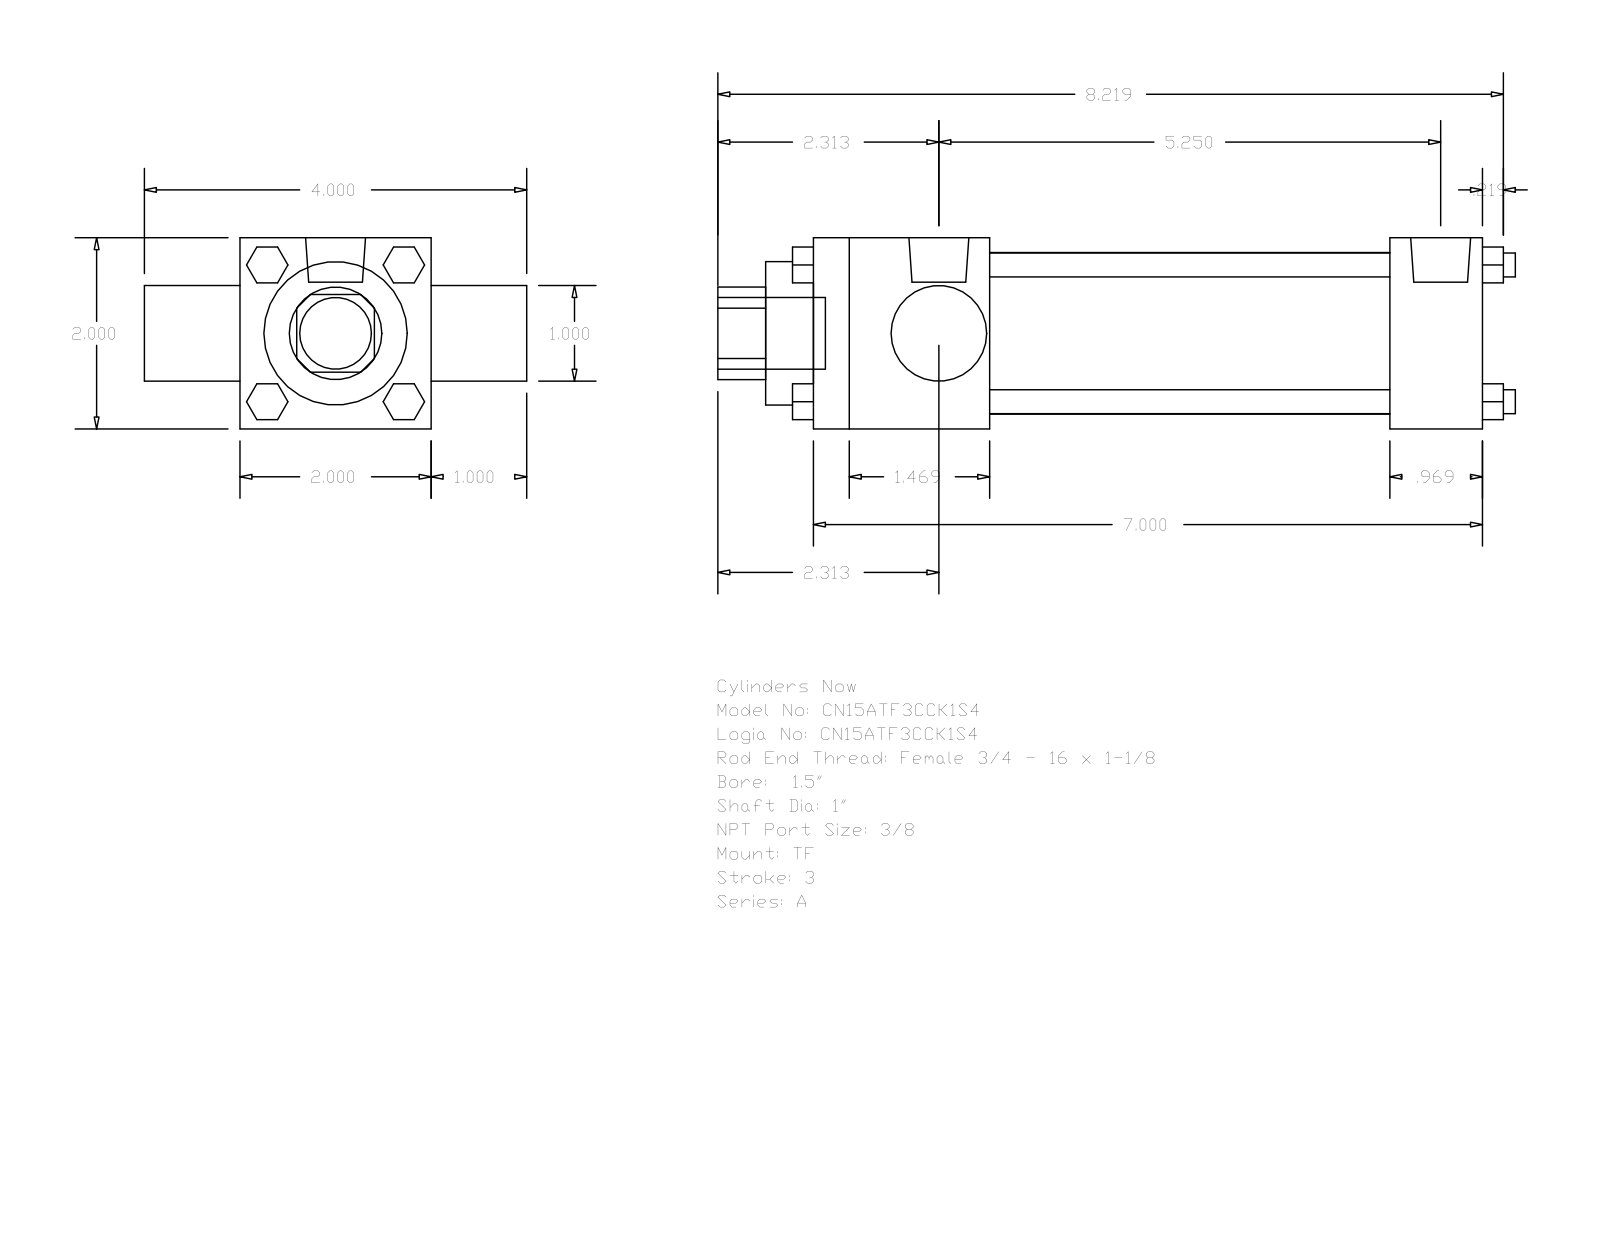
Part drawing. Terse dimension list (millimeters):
name: A_TF__0150_1
written by: GSSL Pune (CONFIG_CONTROL_DESIGN)
unit: mm
bodies: 0 solids, 120 faces (92 planar, 28 cylindrical, 0 other)
size: 211.93 × 101.6 × 50.8
holes: 2× ⌀25.4, 1× ⌀38.1, 1× ⌀42.93
bosses: 4× ⌀6.35, 3× ⌀5.56, 2× ⌀15.93, 1× ⌀19.05
rounds: 1× R12.29
face distances: 50.8, 25.4, 177.8, 76.2, 46.83, 153.19, 106.36, 130.97, 24.61, 12.7
